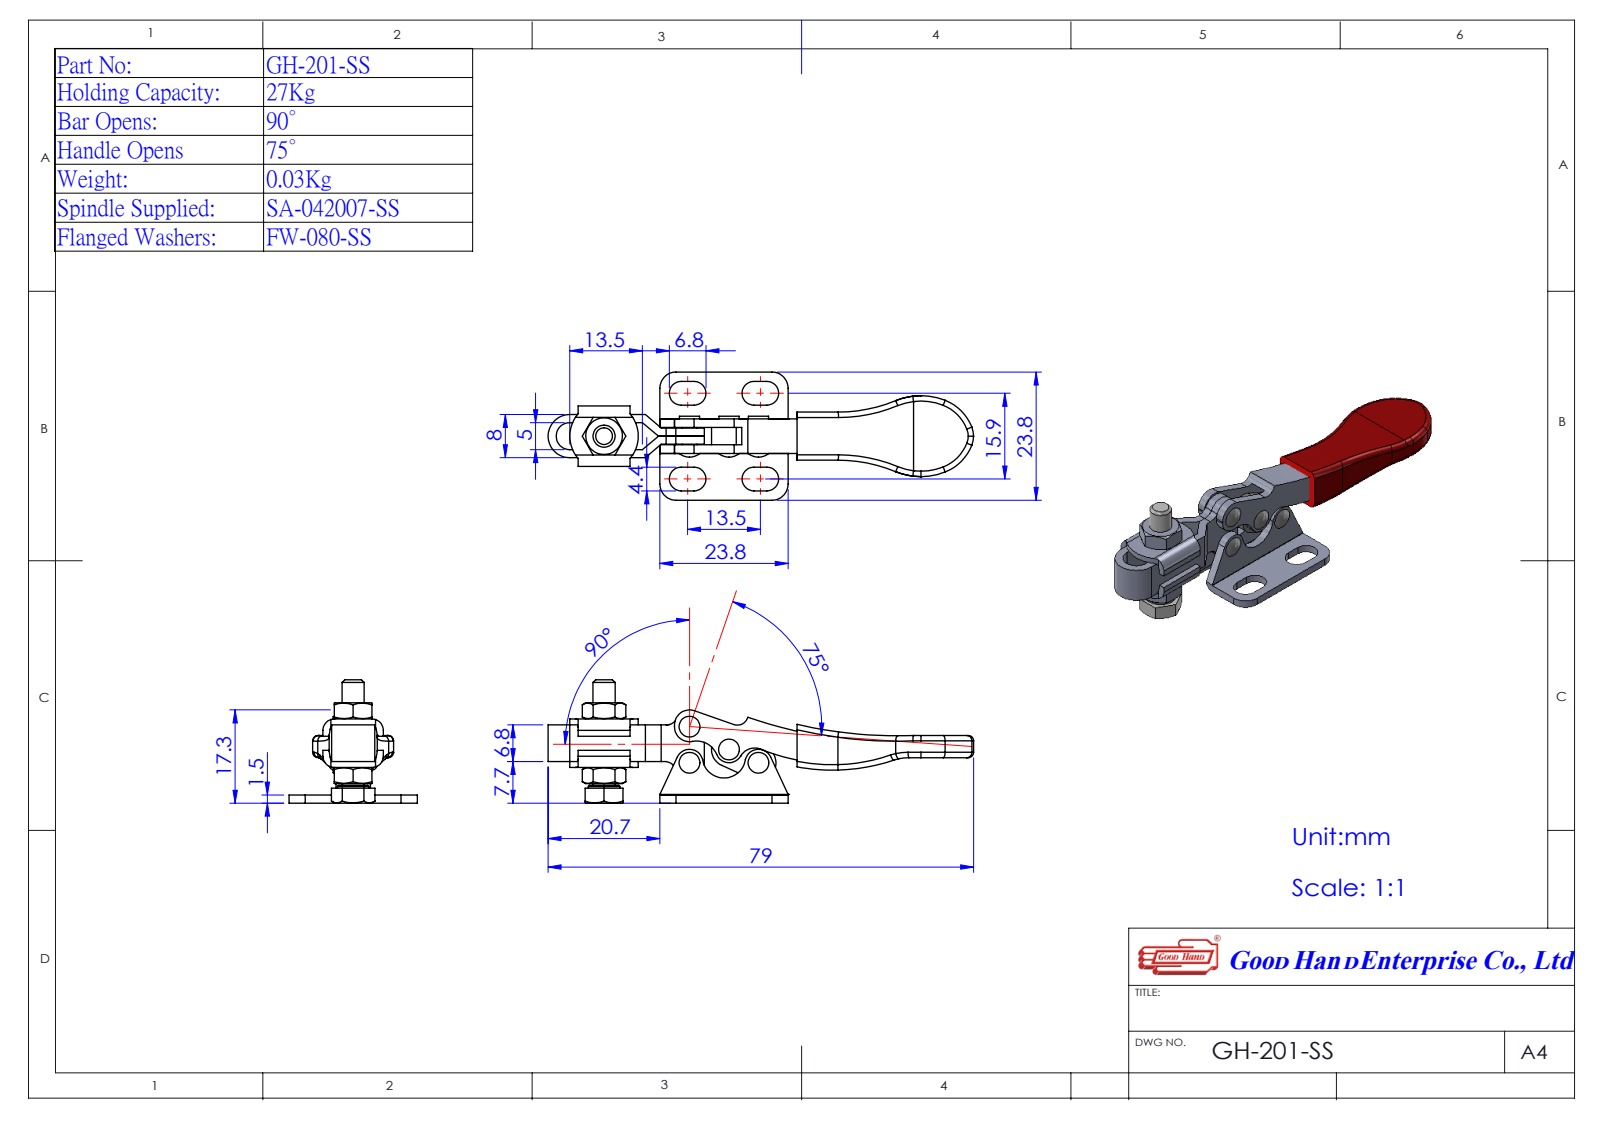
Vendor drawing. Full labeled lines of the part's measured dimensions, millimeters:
Part name (STEP PRODUCT): Group5^493783(GH-201); 493783(GH-201); Group4^493783(GH-201); 120108-1-1^493783(GH-201) (+2 more)
STEP written by: SolidWorks 2016 (AUTOMOTIVE_DESIGN)
Units: millimetres
Bodies: 4 solids, 284 faces (127 planar, 145 cylindrical, 12 other)
Overall size (bounding box): 79 × 23.8 × 22.9
Volume: 2 784 mm³ · Surface area: 7 119 mm²
Round holes (diameter × count): ⌀2.5 ×4
Round bosses / shafts (diameter × count): ⌀3.75 ×4, ⌀2.75 ×2, ⌀5.8 ×1, ⌀4.1 ×1
Partial cylindrical surfaces — rounded edges, fillets, slot ends (radius × count): R2.2 ×8, R1 ×4, R2.1 ×4, R2.5 ×4, R4 ×4, R2.8 ×3, R1.61 ×2, R3.25 ×2
Main face-to-face distances: 1.6, 3.2, 1.5, 4.8, 1.26, 2.86, 4, 2.5, 6.4, 1.96
Hole centre spacings: 6, 6.7, 7.73, 8.47, 12.8, 14.45
